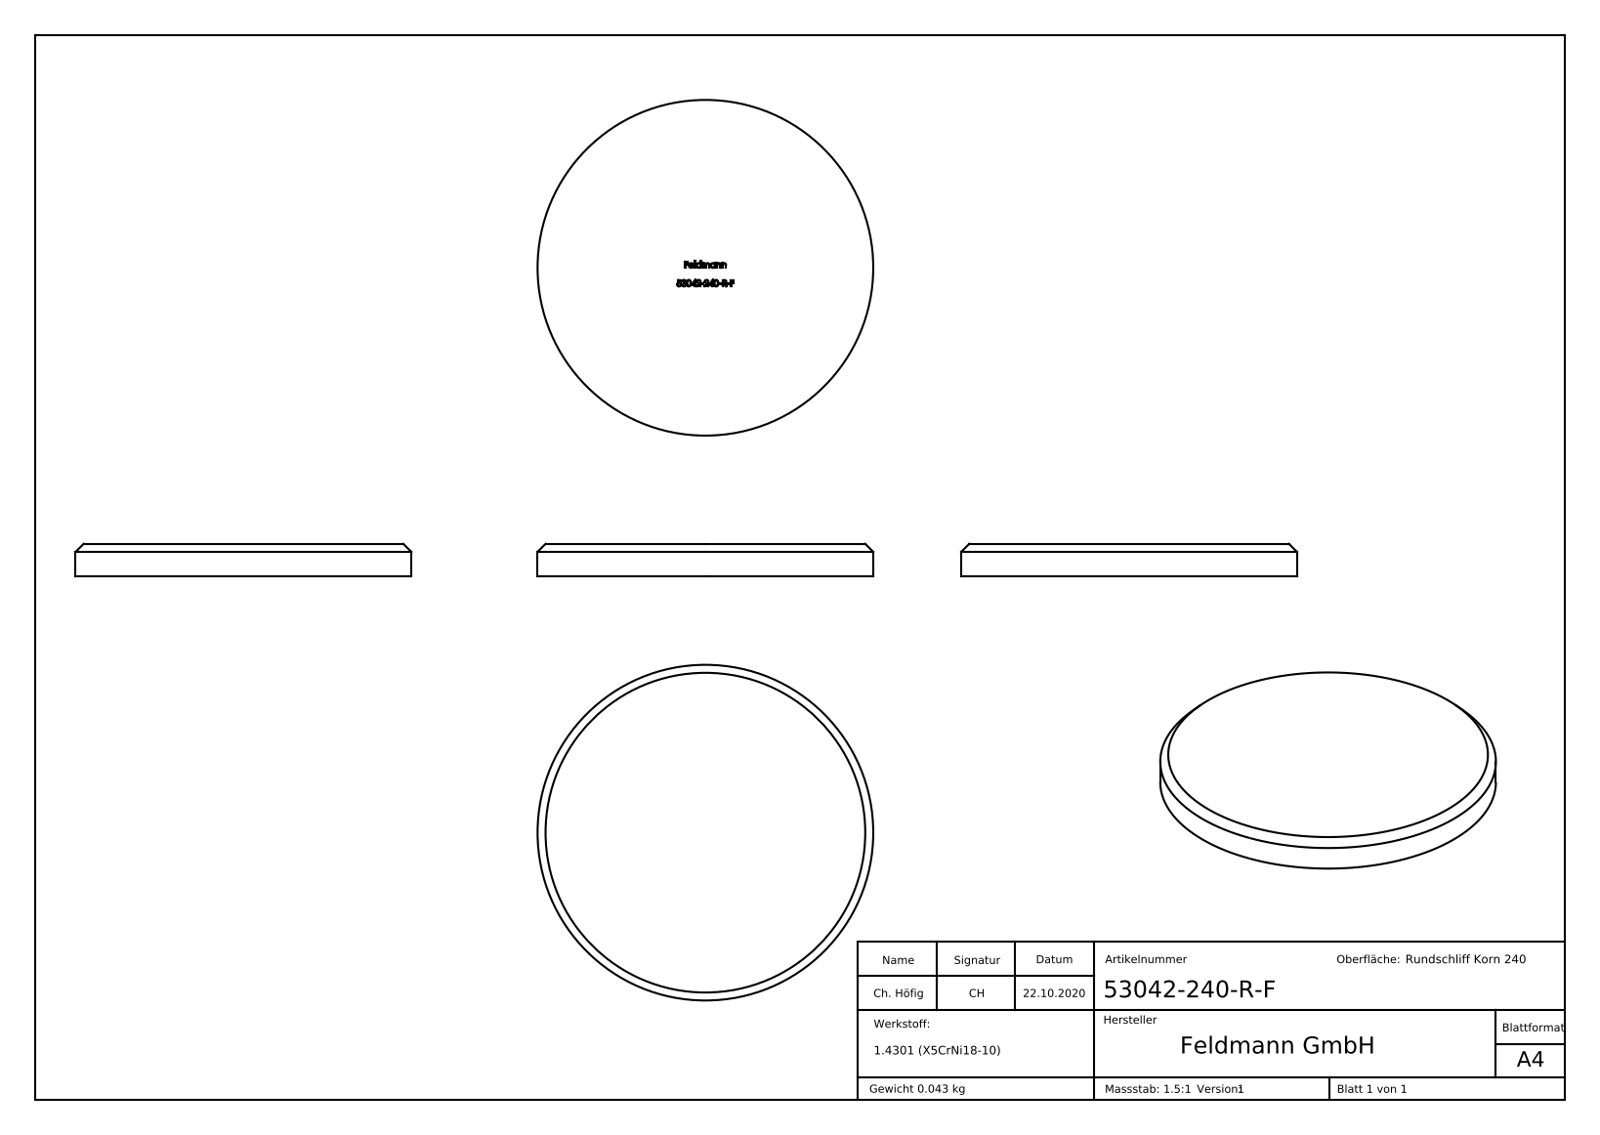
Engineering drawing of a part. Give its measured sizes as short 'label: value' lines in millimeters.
name: 53042-240-R-F
written by: SolidWorks 2018 (CONFIG_CONTROL_DESIGN)
unit: mm
bodies: 1 solid, 274 faces (165 planar, 2 cylindrical, 107 other)
size: 42 × 42 × 4
volume: 5 477 mm³; area: 3 227 mm²
bosses: 1× ⌀42
face distances: 4, 3.9, 2.32, 1.21, 0.71, 2.2, 2.24, 3.49, 0.79, 1.29
